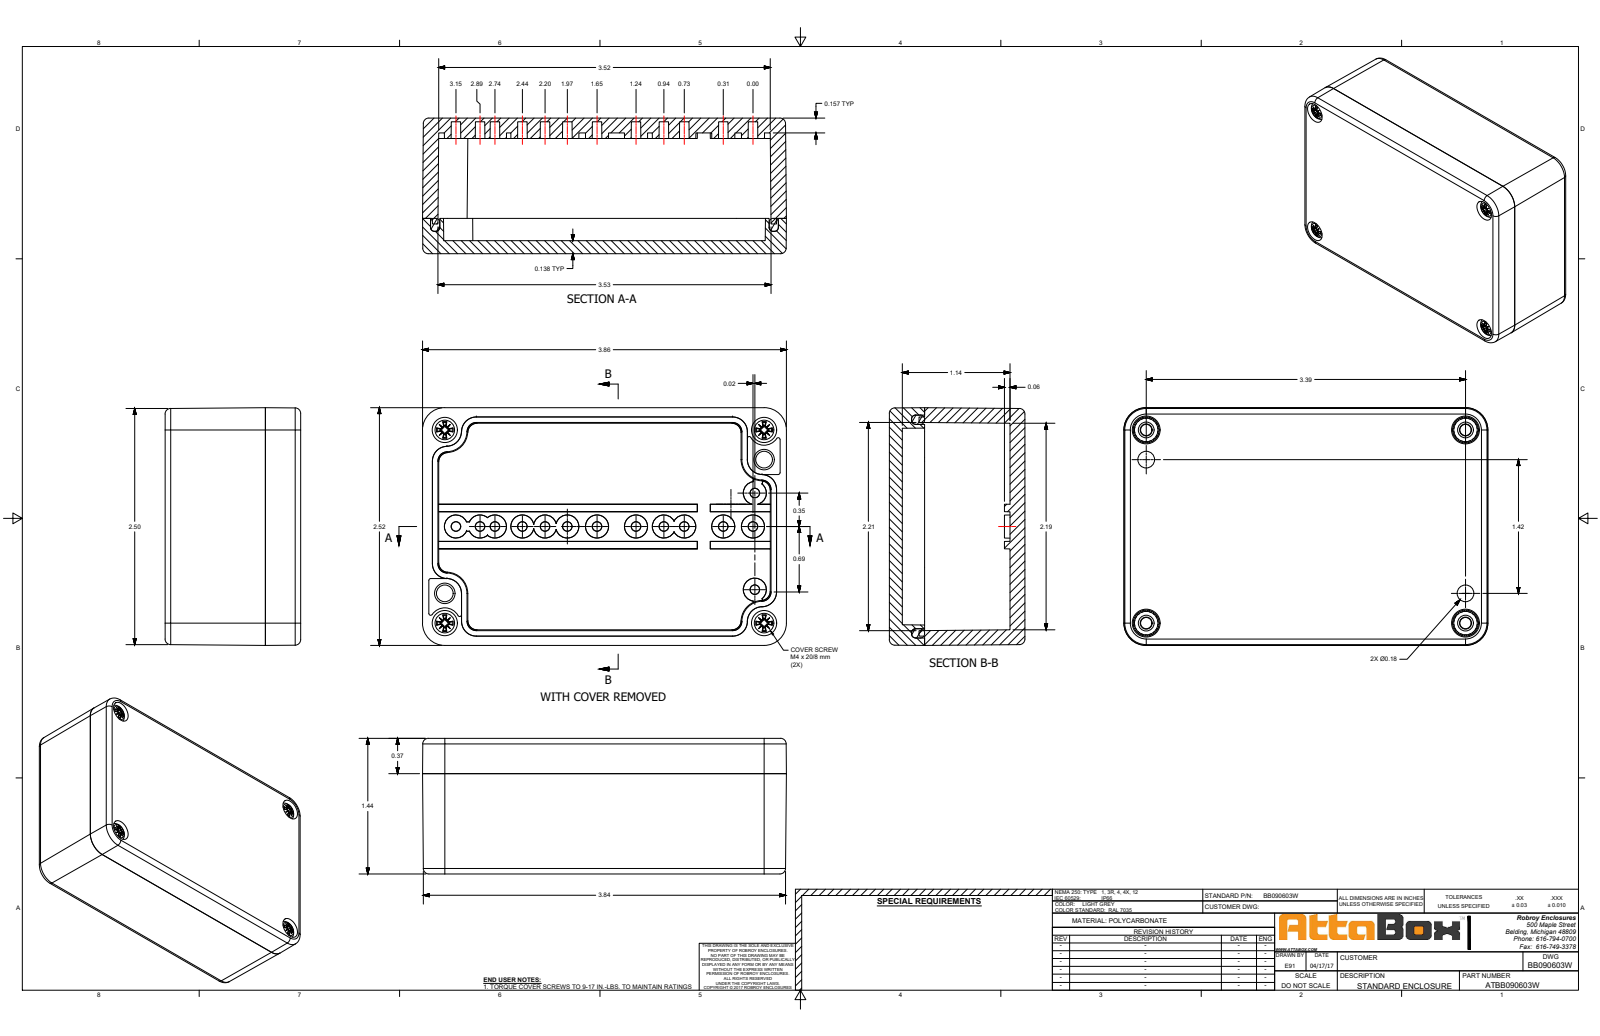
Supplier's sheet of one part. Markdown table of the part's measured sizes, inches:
| quantity | value |
| --- | --- |
| part name | BB090603W |
| STEP written by | SolidWorks 2018 (AUTOMOTIVE_DESIGN) |
| units | inches |
| bodies | 11 solids, 1532 faces (585 planar, 332 cylindrical, 615 other) |
| overall size | 3.858 × 2.52 × 1.437 |
| volume | 5.406 in³ |
| surface area | 90.18 in² |
| round holes (diameter × count) | 0.177 × 6, 0.128 × 4, 0.189 × 4, 0.201 × 4, 0.276 × 4, 0.291 × 4, 0.295 × 4 |
| round bosses / shafts (diameter × count) | 0.268 × 4, 0.173 × 4, 0.157 × 4, 0.13 × 4 |
| partial cylindrical surfaces (radius × count) | 0.043 × 24, 0.039 × 14, 0.059 × 8, 0.02 × 6, 0.098 × 4, 0.102 × 4, 0.124 × 4, 0.138 × 4 |
| main face-to-face distances | 0.157, 1.437, 0.138, 1.299, 1.142, 1.28, 0.906, 0.236, 0.374, 1.063 |
| hole center spacings | 0.315, 1.732, 2.047, 3.386, 3.4, 3.803, 3.957, 3.67 |
